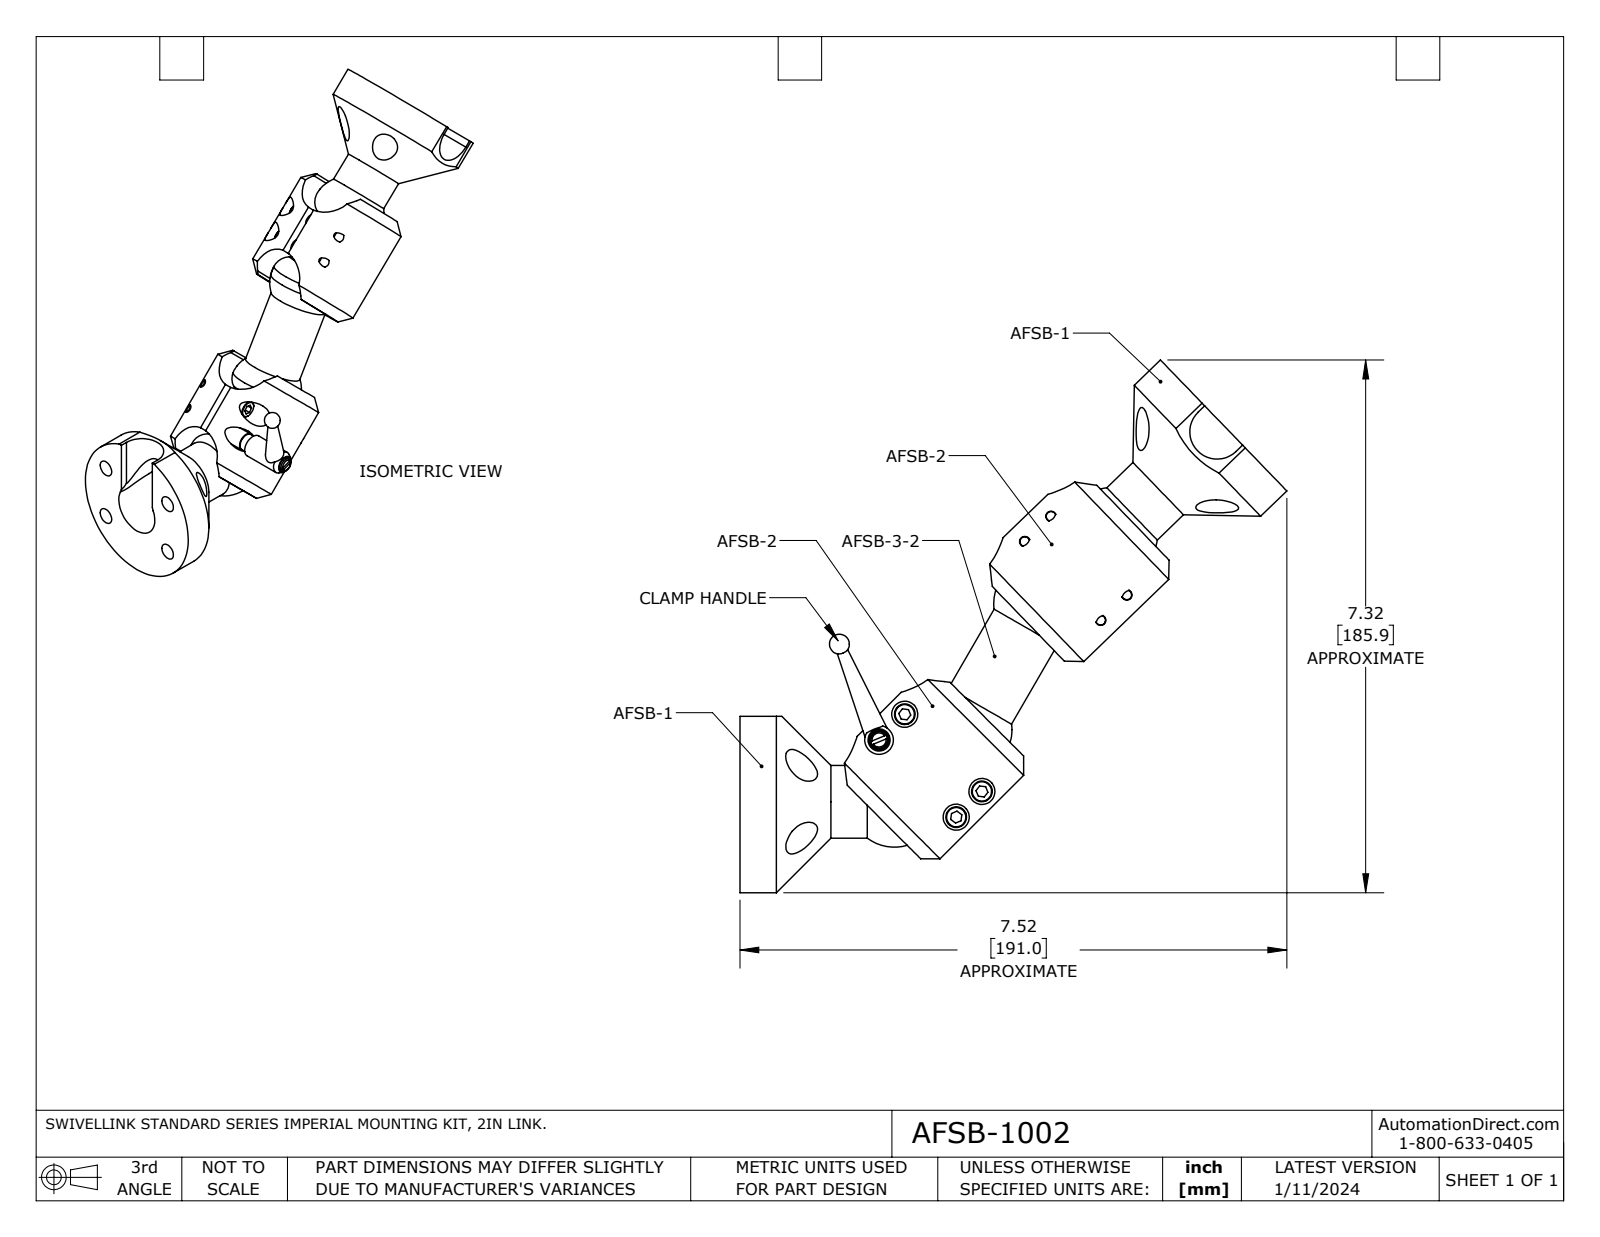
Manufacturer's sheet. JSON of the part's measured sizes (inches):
{"part_name": "AFSB-1002", "step_written_by": "SolidWorks 2023 (AUTOMOTIVE_DESIGN)", "units": "inches", "bodies": {"solids": 18, "faces": 307, "planar": 145, "cylindrical": 99, "other": 63}, "overall_size": [7.519, 7.32, 3.313], "volume_in3": 14.48, "surface_area_in2": 136.9, "round_holes": [[0.145, 8], [0.221, 8], [0.281, 8], [0.359, 8], [0.437, 8], [0.875, 3], [0.192, 1], [0.243, 1], [1.125, 1], [1.125, 1]], "round_bosses_or_shafts": [[0.19, 8], [0.285, 6], [1, 3], [2.5, 2], [2, 2], [0.285, 2], [1.24, 1], [0.395, 1]], "partial_cylinders_radius": [[0.525, 4], [0.375, 2]], "face_to_face_distances": [0.125, 0.313, 0.187, 2, 1.825, 2, 3.825, 0.5, 0.25, 2.25], "hole_center_spacings": [1, 1.5, 1.803, 0.902, 1.581, 0.5, 0.897, 0.899]}
